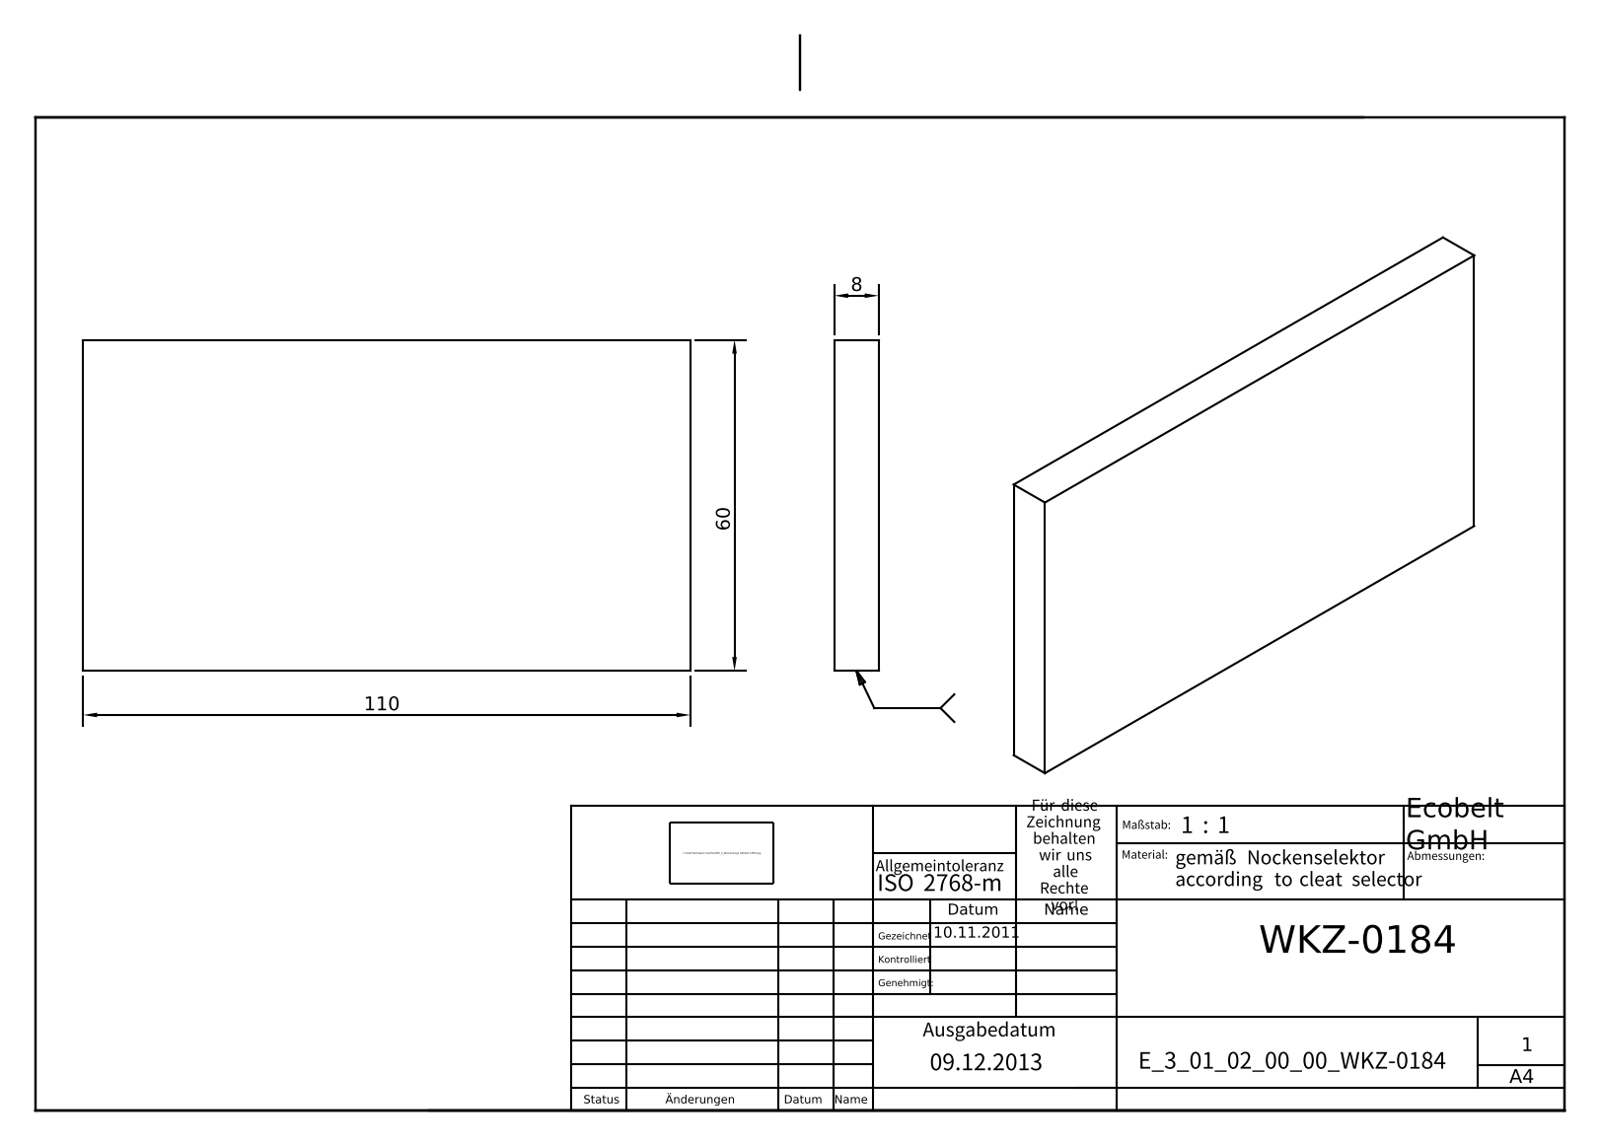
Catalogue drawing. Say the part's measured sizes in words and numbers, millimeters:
The part is named "E_3_01_02_00_00_WKZ-0184". Its 3-D file was written by "Autodesk Inventor 2021 (AUTOMOTIVE_DESIGN)". It is 1 solid with 6 faces: 6 planar, 0 cylindrical and 0 other. Overall it measures 110 by 60 by 8 millimeters. Its volume is 52 800 cubic millimeters and its surface area 15 920 square millimeters. The main face-to-face distances are 8, 60, 110.
